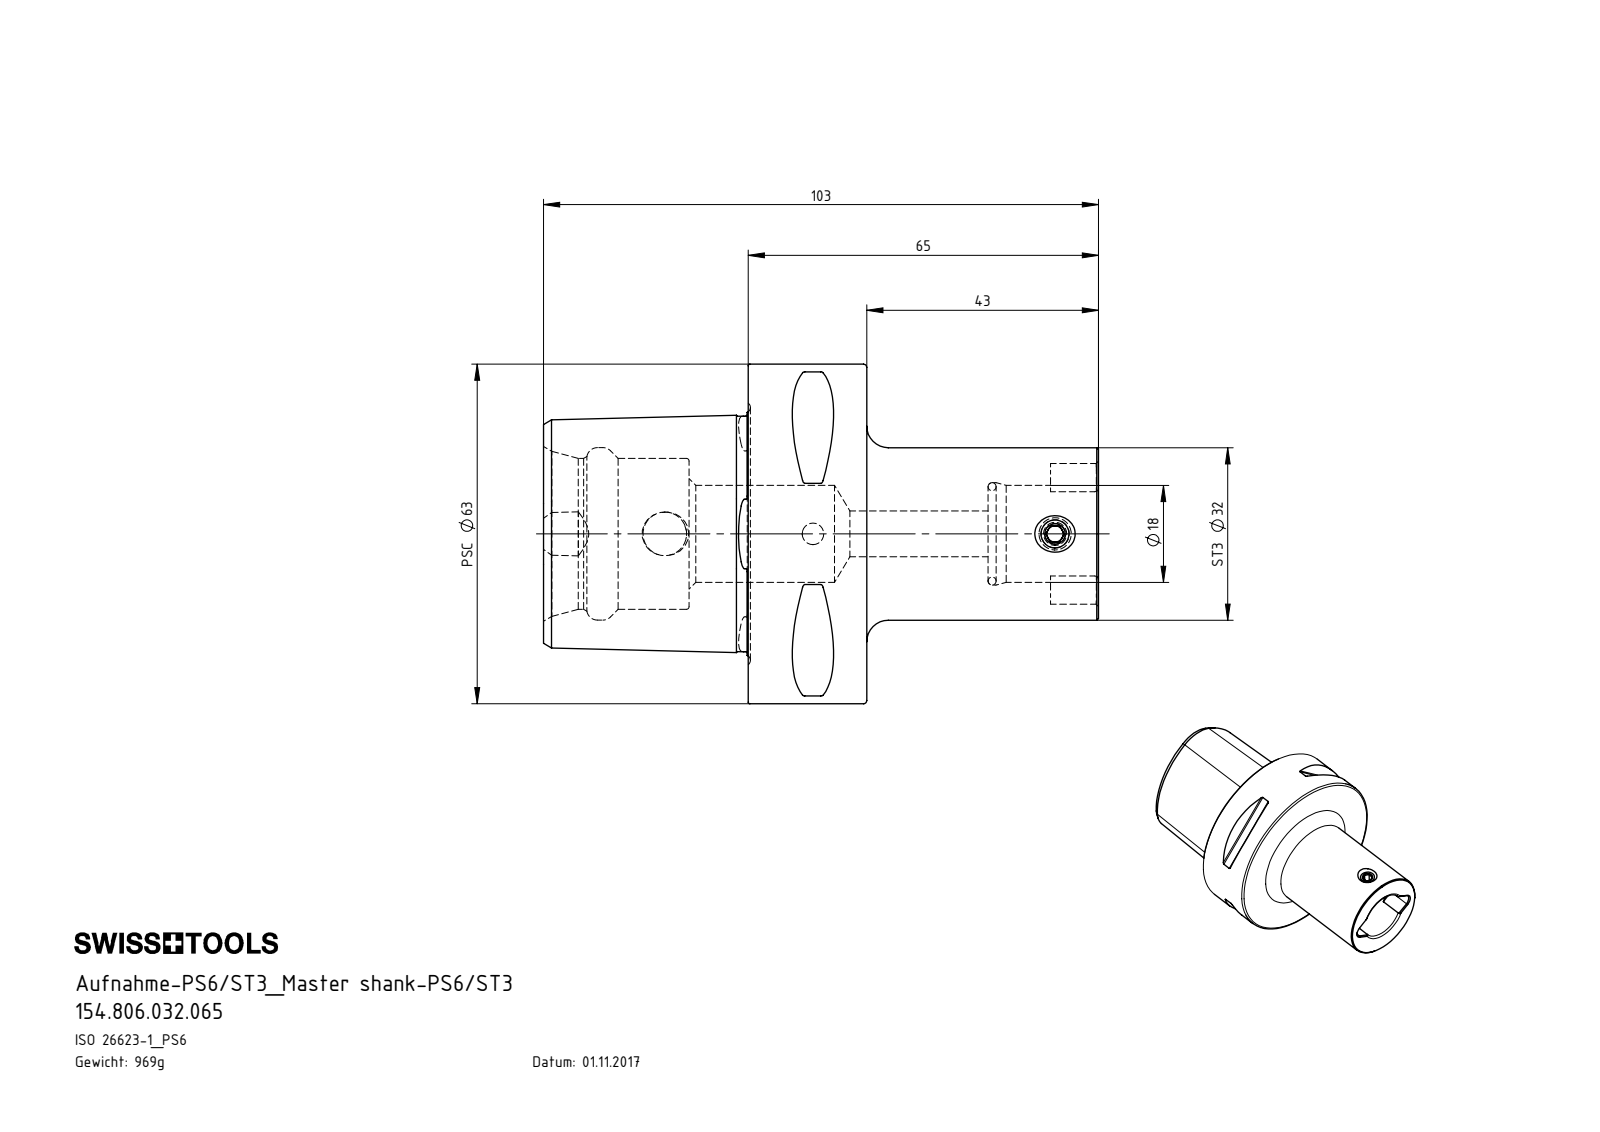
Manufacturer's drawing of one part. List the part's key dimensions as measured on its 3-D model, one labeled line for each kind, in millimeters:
Part name (STEP PRODUCT): PS6-ST3.K01.065_B; PS6.ST3.K01.065; ST3-ER1.001.008_A; DIN 3771 - 16x1.5_gespannt1
STEP written by: SolidWorks 2017 (AUTOMOTIVE_DESIGN)
Units: millimetres
Bodies: 3 solids, 133 faces (43 planar, 26 cylindrical, 64 other)
Overall size (bounding box): 103 × 63 × 63
Volume: 123 530 mm³ · Surface area: 26 486 mm²
Round holes (diameter × count): ⌀3 ×1, ⌀4 ×1, ⌀5.25 ×1, ⌀8.1 ×1, ⌀8.5 ×1, ⌀18 ×1, ⌀19 ×1, ⌀28 ×1, ⌀32 ×1
Round bosses / shafts (diameter × count): ⌀63 ×1, ⌀6 ×1
Partial cylindrical surfaces — rounded edges, fillets, slot ends (radius × count): R0.5 ×8, R2.5 ×2, R6 ×1
Main face-to-face distances: 22, 38, 60, 103, 65, 43, 24.88, 27, 11, 33
Hole centre spacings: 27.5, 44.95, 72.45
